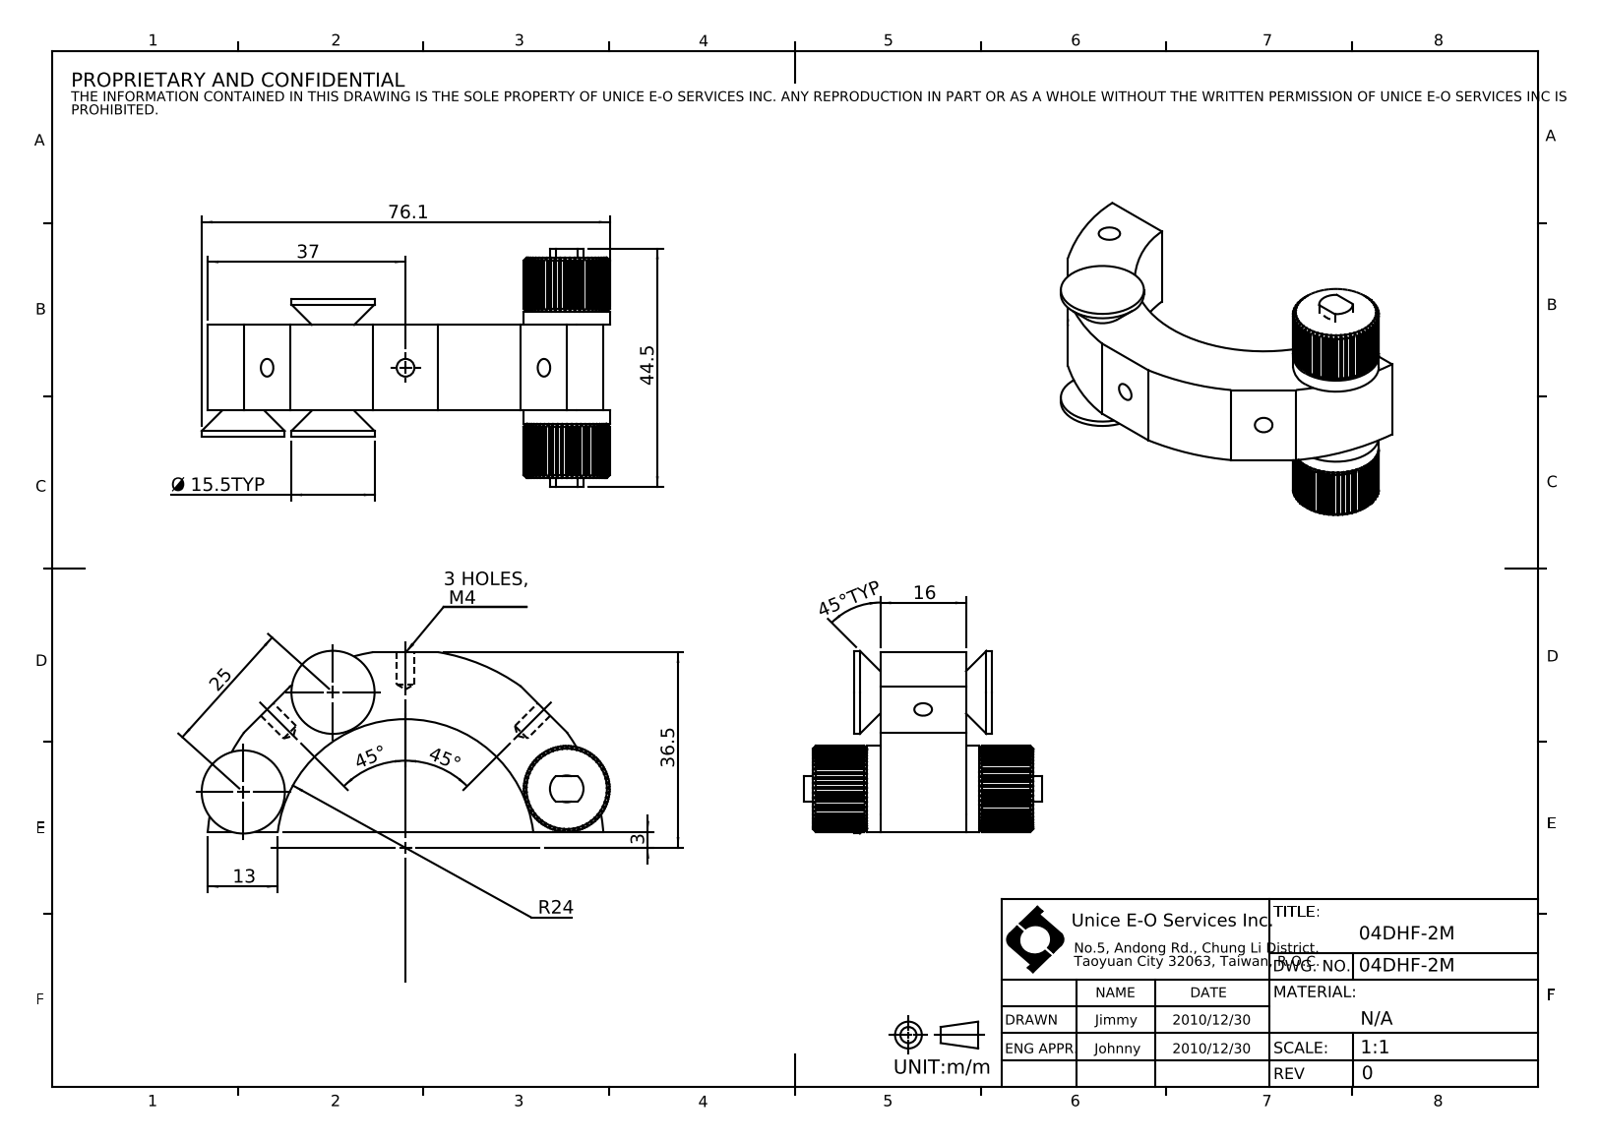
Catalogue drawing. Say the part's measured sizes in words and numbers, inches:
The part is named "04DHF-2M". Its 3-D file was written by "SolidWorks 2016 (CONFIG_CONTROL_DESIGN)". It is 9 solids with 653 faces: 260 planar, 161 cylindrical and 232 other. Overall it measures 2.994 by 1.752 by 1.342 inches. Its volume is 1.516 cubic inches and its surface area 20.3 square inches. Round holes: 3 of diameter 0.13, 1 of diameter 0.157, 1 of diameter 0.197, 1 of diameter 0.246, 1 of diameter 0.252, 1 of diameter 0.394. Round bosses or shafts: 2 of diameter 0.61, 1 of diameter 0.63, 1 of diameter 0.319, 1 of diameter 0.157. Partial cylindrical surfaces (rounded edges, fillets, slot ends): 1 of radius 0.945, 1 of radius 1.457. The main face-to-face distances are 0.63, 0.189, 0.819, 0.098, 0.728, 0.091, 0.917, 0.303, 0.394, 0.492. The hole center spacings are 2.374.
